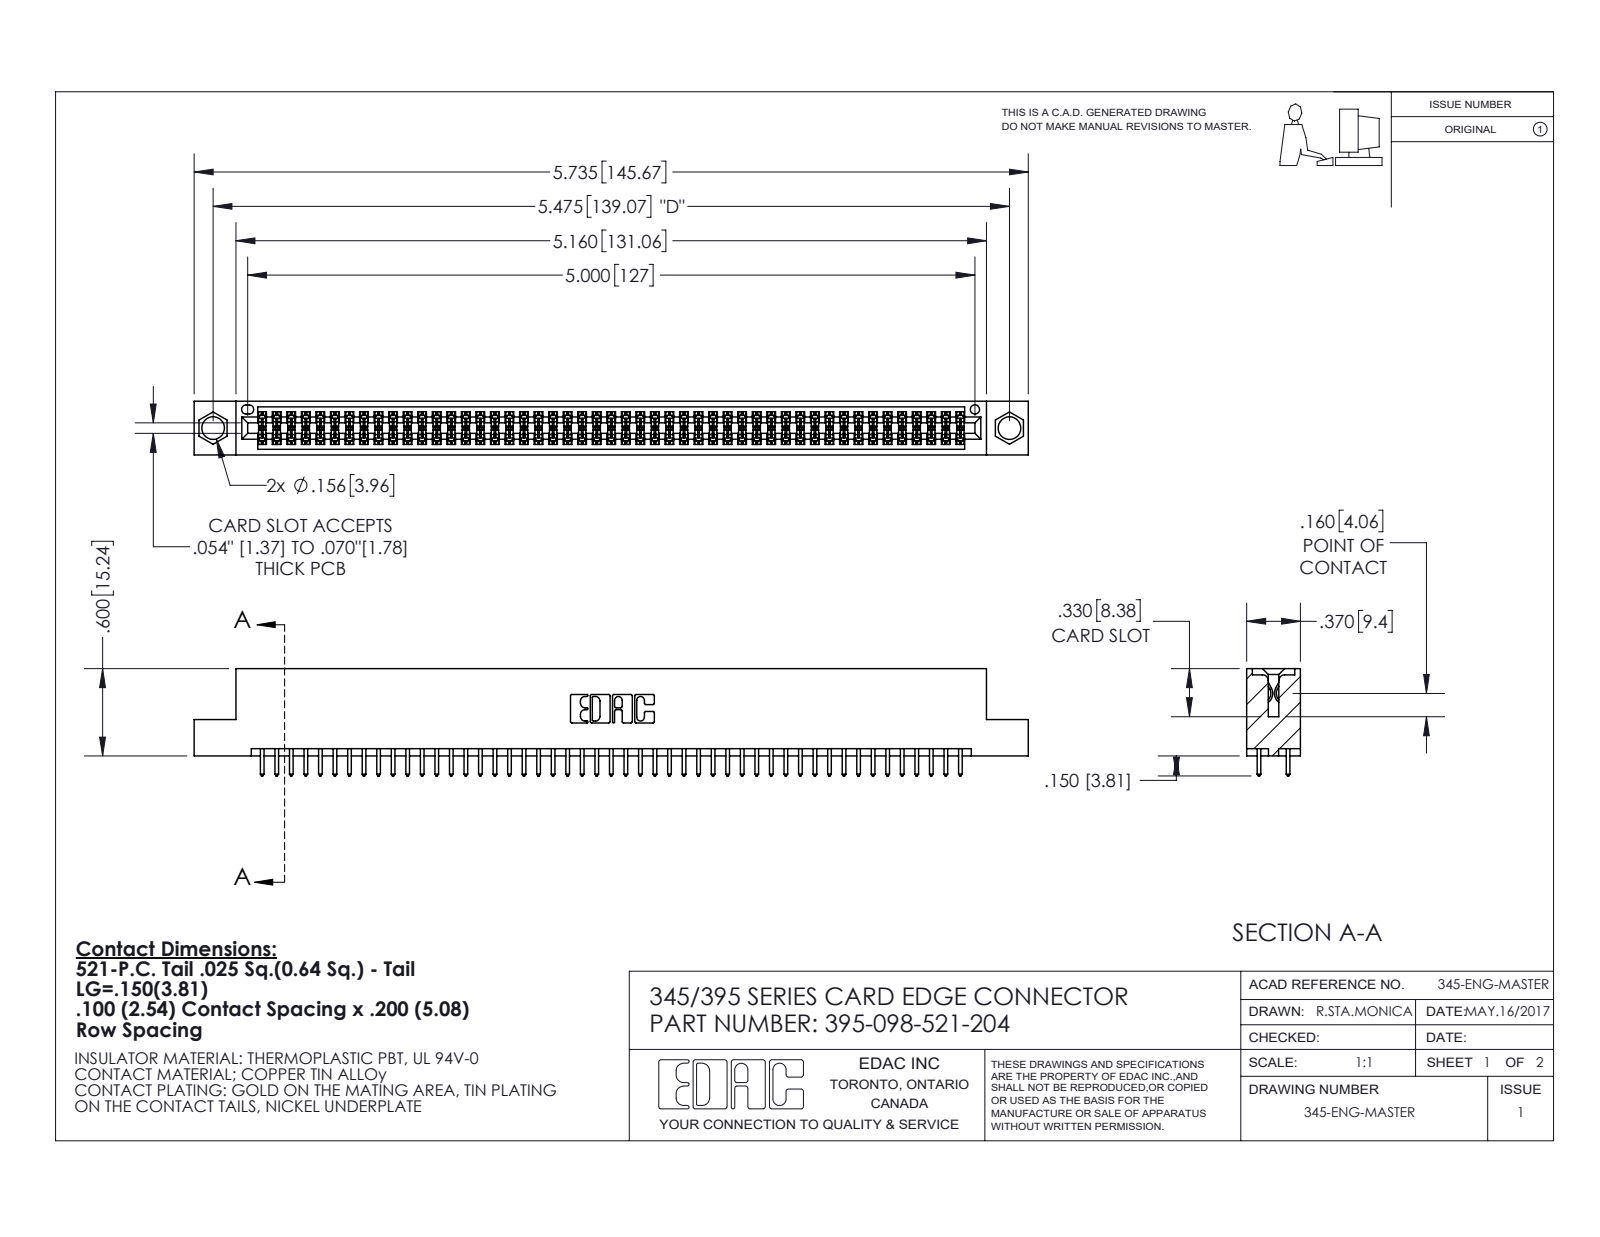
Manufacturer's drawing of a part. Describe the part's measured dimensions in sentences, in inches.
The part is named "345-292-001_345-293-121; 345 Part_Flush Mounting Lugs - 0.156 Dia-TI; 395-098-521-204". Its 3-D file was written by "SolidWorks 2020 (CONFIG_CONTROL_DESIGN)". It is 99 solids with 5040 faces: 3328 planar, 1712 cylindrical and 0 other. Overall it measures 5.735 by 0.737 by 0.37 inches. Its volume is 0.859 cubic inches and its surface area 31.81 square inches. Round holes: 2 of diameter 0.156, 1 of diameter 0.064. Partial cylindrical surfaces (rounded edges, fillets, slot ends): 196 of radius 0.006, 98 of radius 0.01, 22 of radius 0.01, 6 of radius 0.007, 6 of radius 0.031, 3 of radius 0.026, 2 of radius 0.014, 2 of radius 0.019. The main face-to-face distances are 0.072, 0.298, 0.2, 0.37, 0.098, 0.272, 0.025, 0.225, 0.175, 0.149. The hole center spacings are 0.27, 5.239, 5.475.
